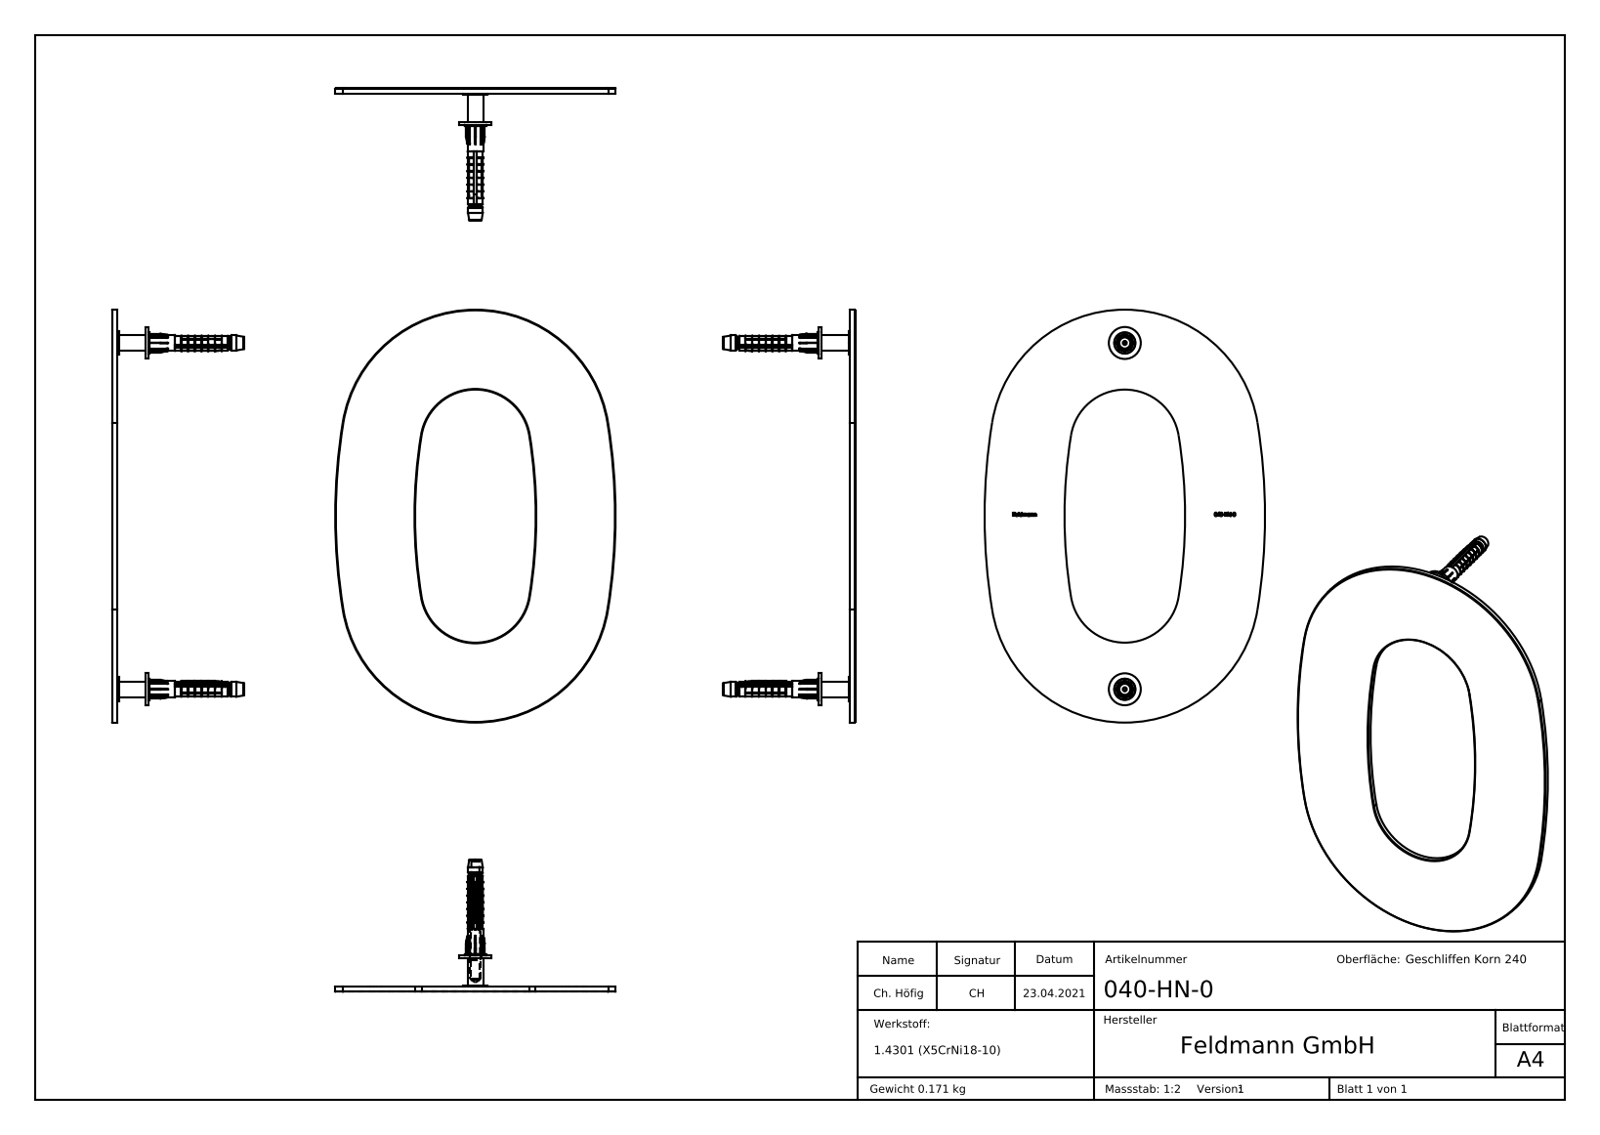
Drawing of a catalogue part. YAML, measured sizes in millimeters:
part_name: "040-HN-X Teil3_040-HN-X Teil3; 040-HN-X Teil4; 040-HN-X Teil2; 040-HN-0 (+5 more)"
step_written_by: "SolidWorks 2018 (CONFIG_CONTROL_DESIGN)"
units: millimeters
bodies: {solids: 7, faces: 1551, planar: 352, cylindrical: 388, other: 811}
overall_size: [10000, 5217.43, 4607.88]
volume: 22561
surface_area: 25552
round_holes:
  - {diameter: 3.3, count: 2}
  - {diameter: 4.3, count: 2}
round_bosses_or_shafts:
  - {diameter: 12, count: 2}
  - {diameter: 9, count: 2}
  - {diameter: 8, count: 2}
  - {diameter: 6, count: 2}
  - {diameter: 5.8, count: 2}
  - {diameter: 5.6, count: 2}
  - {diameter: 4.6, count: 2}
  - {diameter: 4, count: 2}
partial_cylinders:
  - {radius: 0.1, count: 22}
  - {radius: 3.5, count: 2}
  - {radius: 20.45, count: 2}
  - {radius: 50.45, count: 2}
  - {radius: 189.75, count: 2}
  - {radius: 219.75, count: 2}
face_to_face_distances: [2, 11.6, 13.6, 1.1, 10.5, 12.5, 0.5, 2.5, 10, 11.1]
hole_center_spacings: [130]
